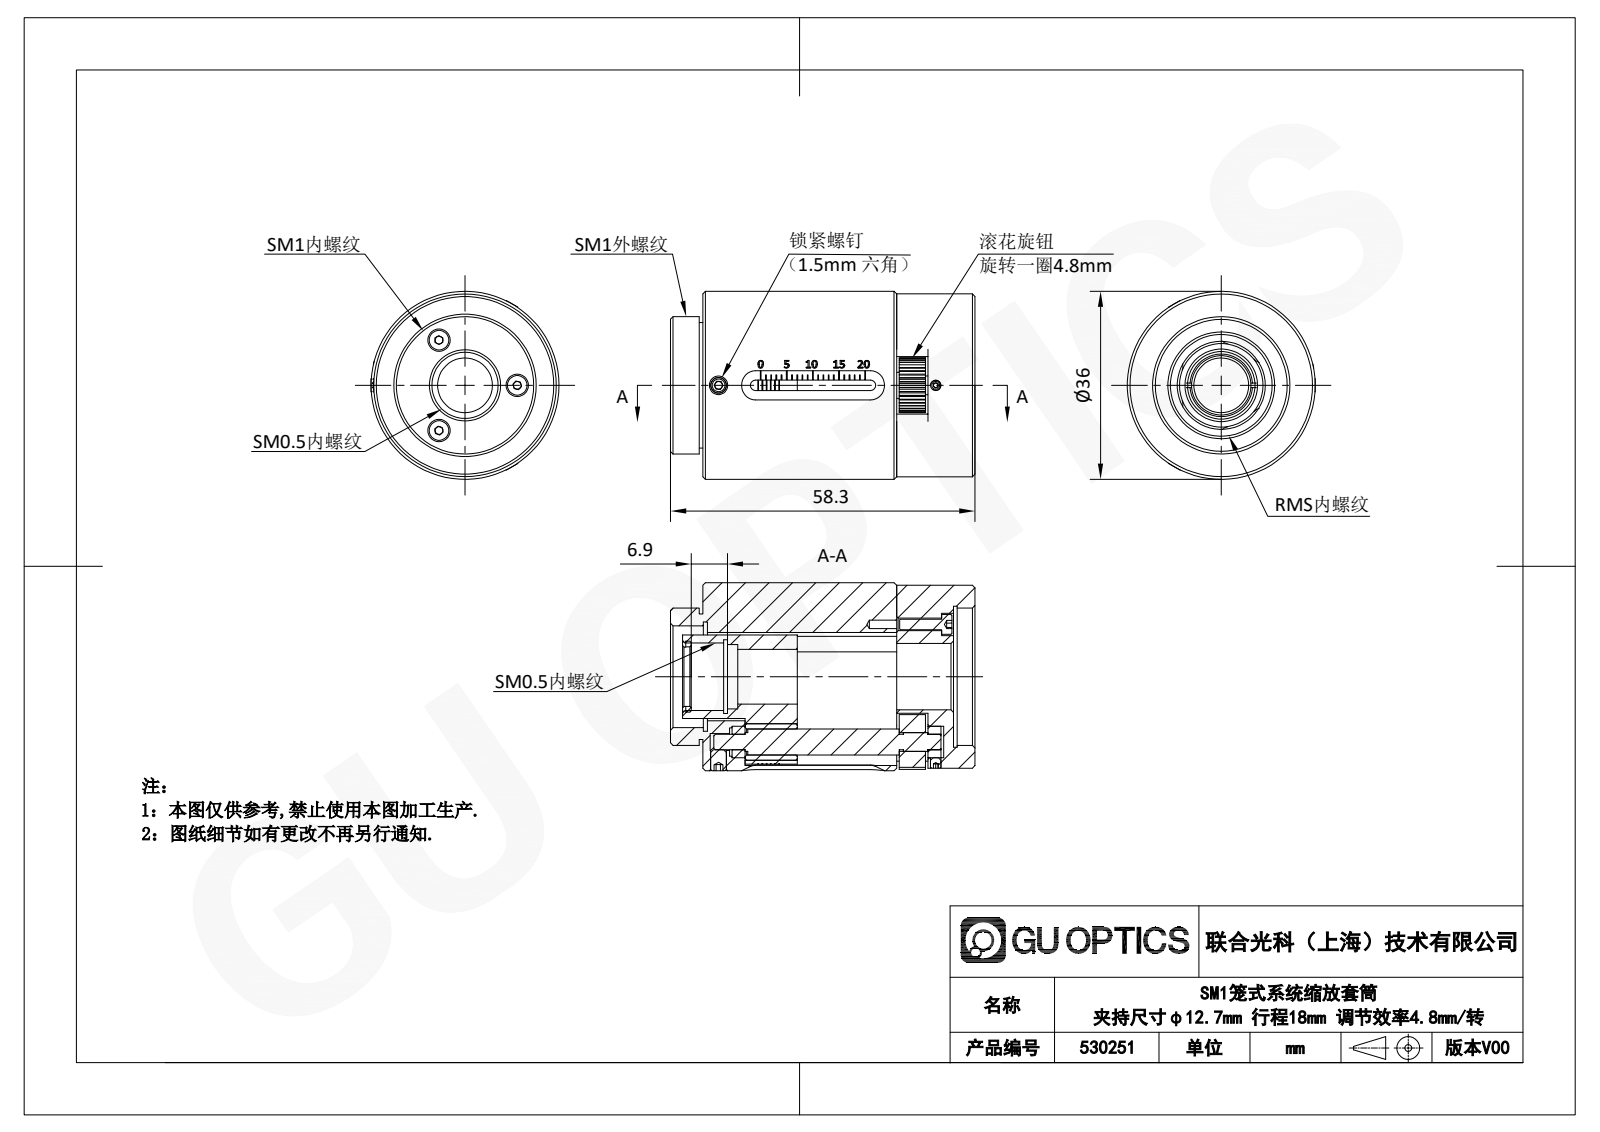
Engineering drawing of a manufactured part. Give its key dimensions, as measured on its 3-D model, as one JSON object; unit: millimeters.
{"part_name": "hex socket set screws with flat point gb1_GB_FASTENER_SCREWS_HSFP M3X4-N; hexagon socket head cap screws gb_GB_FASTENER_SCREWS_HSHCS M2X8-N; hex socket set screws with flat point gb1_GB_FASTENER_SCREWS_HSFP M3X3-N; hex socket set screws with flat point gb1_GB_FASTENER_SCREWS_HSFP M2X2-N (+1 more)", "step_written_by": "SolidWorks 2020 (CONFIG_CONTROL_DESIGN)", "units": "millimeters", "bodies": {"solids": 22, "faces": 758, "planar": 451, "cylindrical": 159, "other": 148}, "overall_size": [58.3, 36, 36], "volume_mm3": 39606, "surface_area_mm2": 22701, "round_holes": [[3, 7], [1.6, 3], [2.4, 3], [4.3, 3], [7, 3], [2, 1], [3.2, 1], [5, 1], [5.4, 1], [6, 1], [10.5, 1], [11.4, 1]], "round_bosses_or_shafts": [[3.8, 3], [2, 3], [36, 1], [35, 1], [26.3, 1], [24, 1], [16, 1], [13.59, 1]], "partial_cylinders_radius": [[2, 12], [1, 4], [4.25, 3], [4.5, 3], [4.15, 1], [5.25, 1], [5.5, 1], [17.99, 1]], "face_to_face_distances": [37.1, 9, 8.1, 10.9, 48, 29, 39.9, 44, 52.1, 15], "hole_center_spacings": [11.46, 10, 12.5, 17.32, 22.5, 21.65, 40.1, 21.66]}
